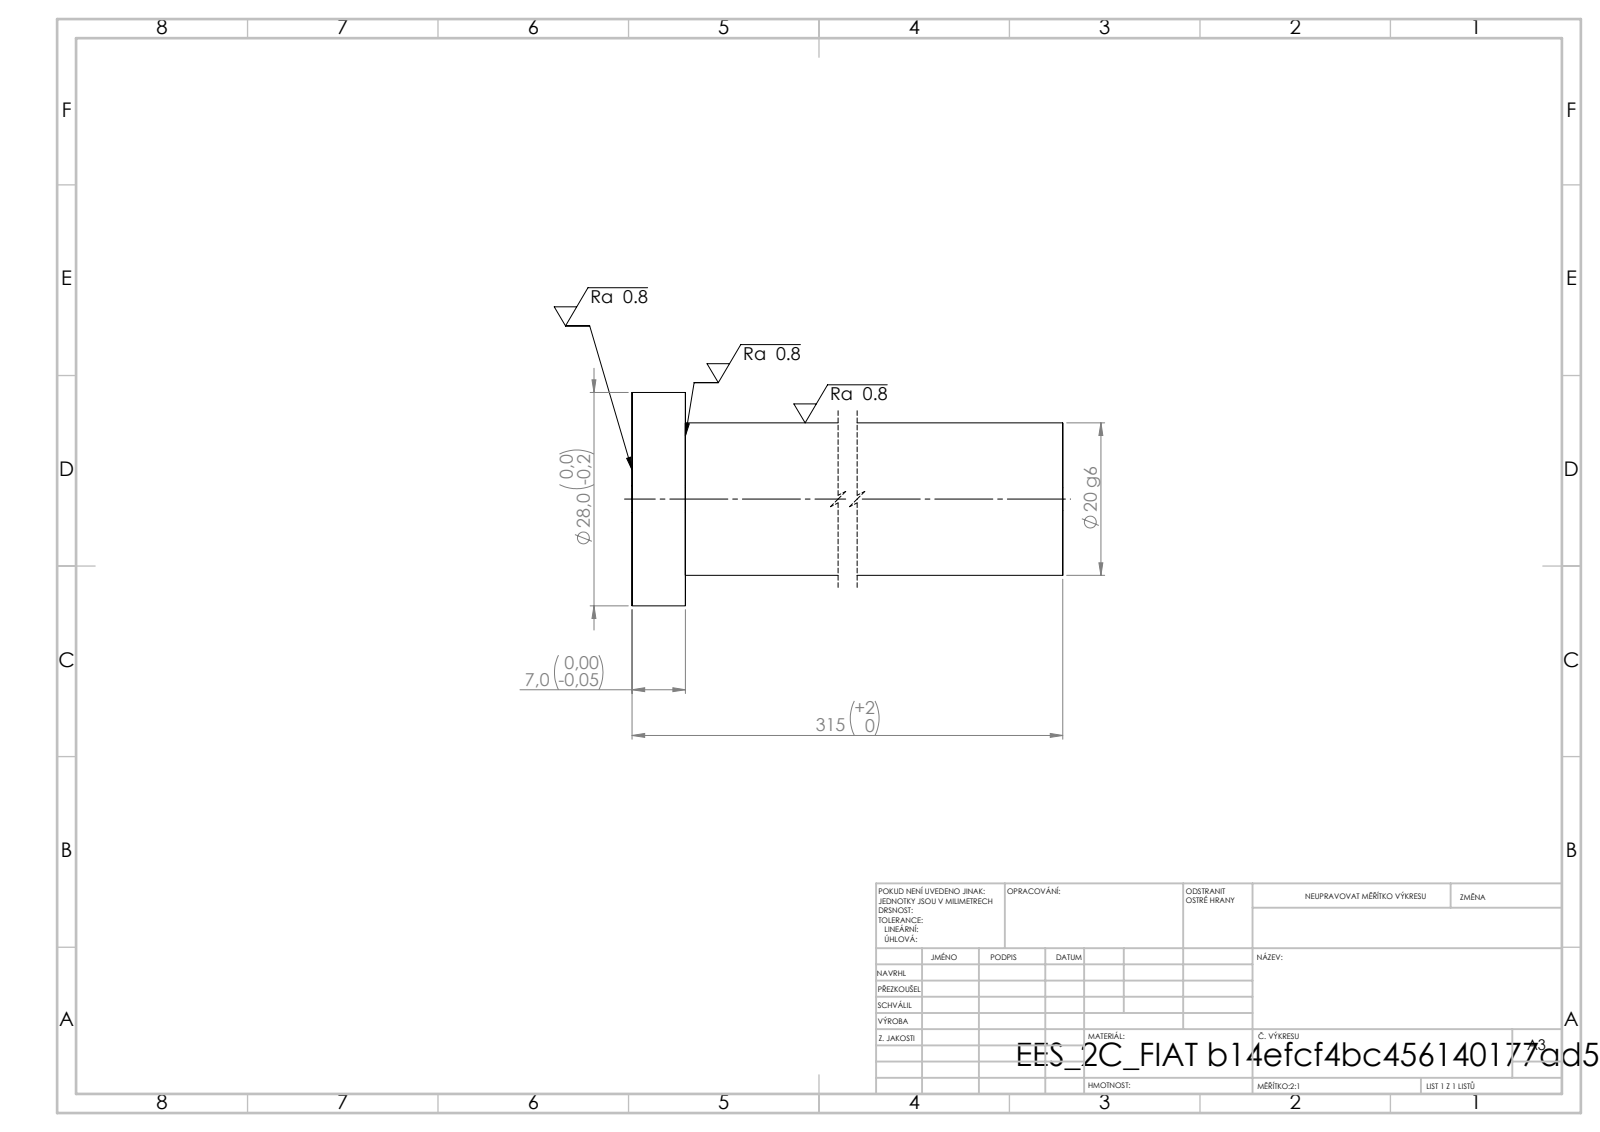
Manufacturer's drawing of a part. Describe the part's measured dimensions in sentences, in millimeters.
Its 3-D file was written by "SolidWorks 2019 (CONFIG_CONTROL_DESIGN)". It is 1 solid with 7 faces: 3 planar, 4 cylindrical and 0 other. Overall it measures 315 by 28 by 28 millimeters. Its volume is 101 071 cubic millimeters and its surface area 21 199 square millimeters. Round bosses or shafts: 1 of diameter 28, 1 of diameter 20. The main face-to-face distances are 315, 7, 308.
